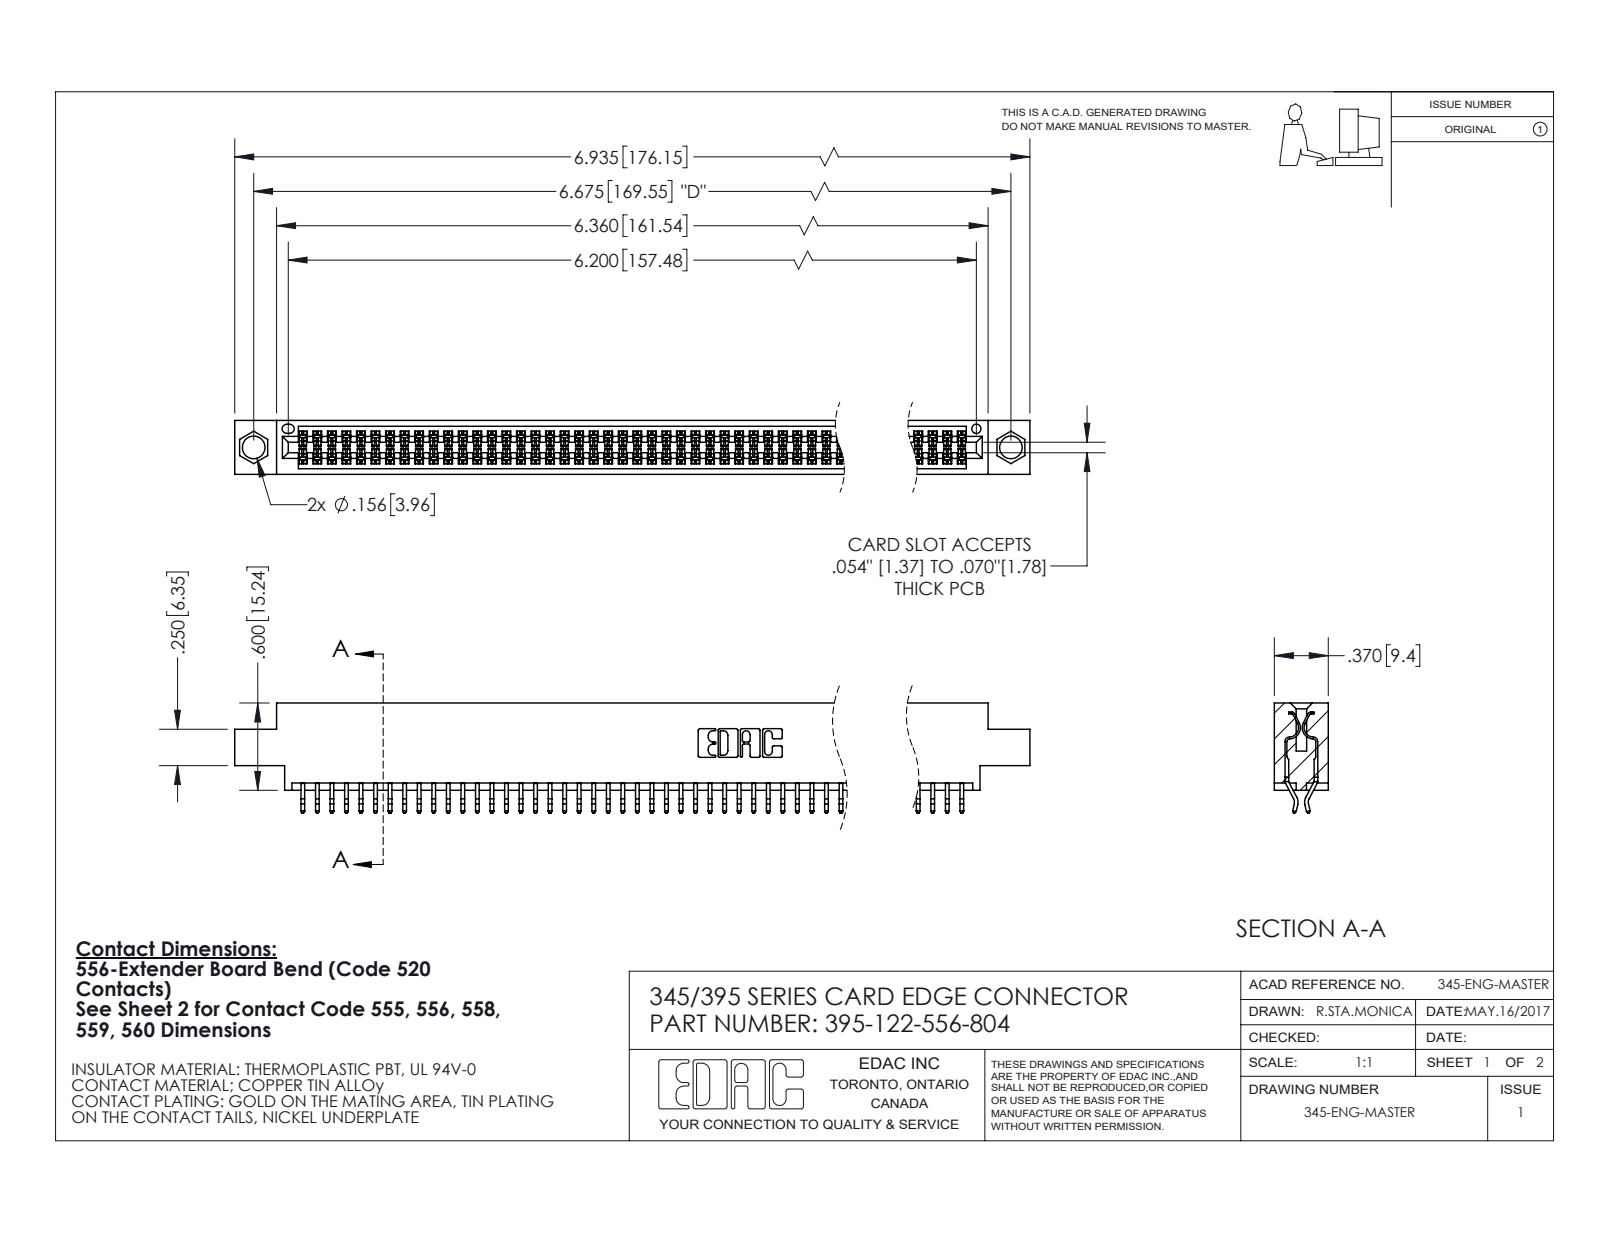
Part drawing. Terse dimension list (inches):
name: 345-292-001_556 Tail; 395-122-556-804; 345 Part_0.170 Offset - 0.156 Dia-TI
written by: SolidWorks 2020 (CONFIG_CONTROL_DESIGN)
unit: in
bodies: 123 solids, 6976 faces (4612 planar, 2364 cylindrical, 0 other)
size: 6.935 × 0.757 × 0.37
volume: 1.041 in³; area: 39.49 in²
holes: 2× ⌀0.156, 1× ⌀0.064
rounds: 244× R0.006, 22× R0.01, 6× R0.007, 6× R0.031, 3× R0.026, 2× R0.01, 2× R0.014, 2× R0.019
face distances: 0.072, 0.298, 0.37, 0.2, 0.025, 0.098, 0.272, 0.225, 0.175, 0.149
hole spacings: 0.27, 6.439, 6.675
